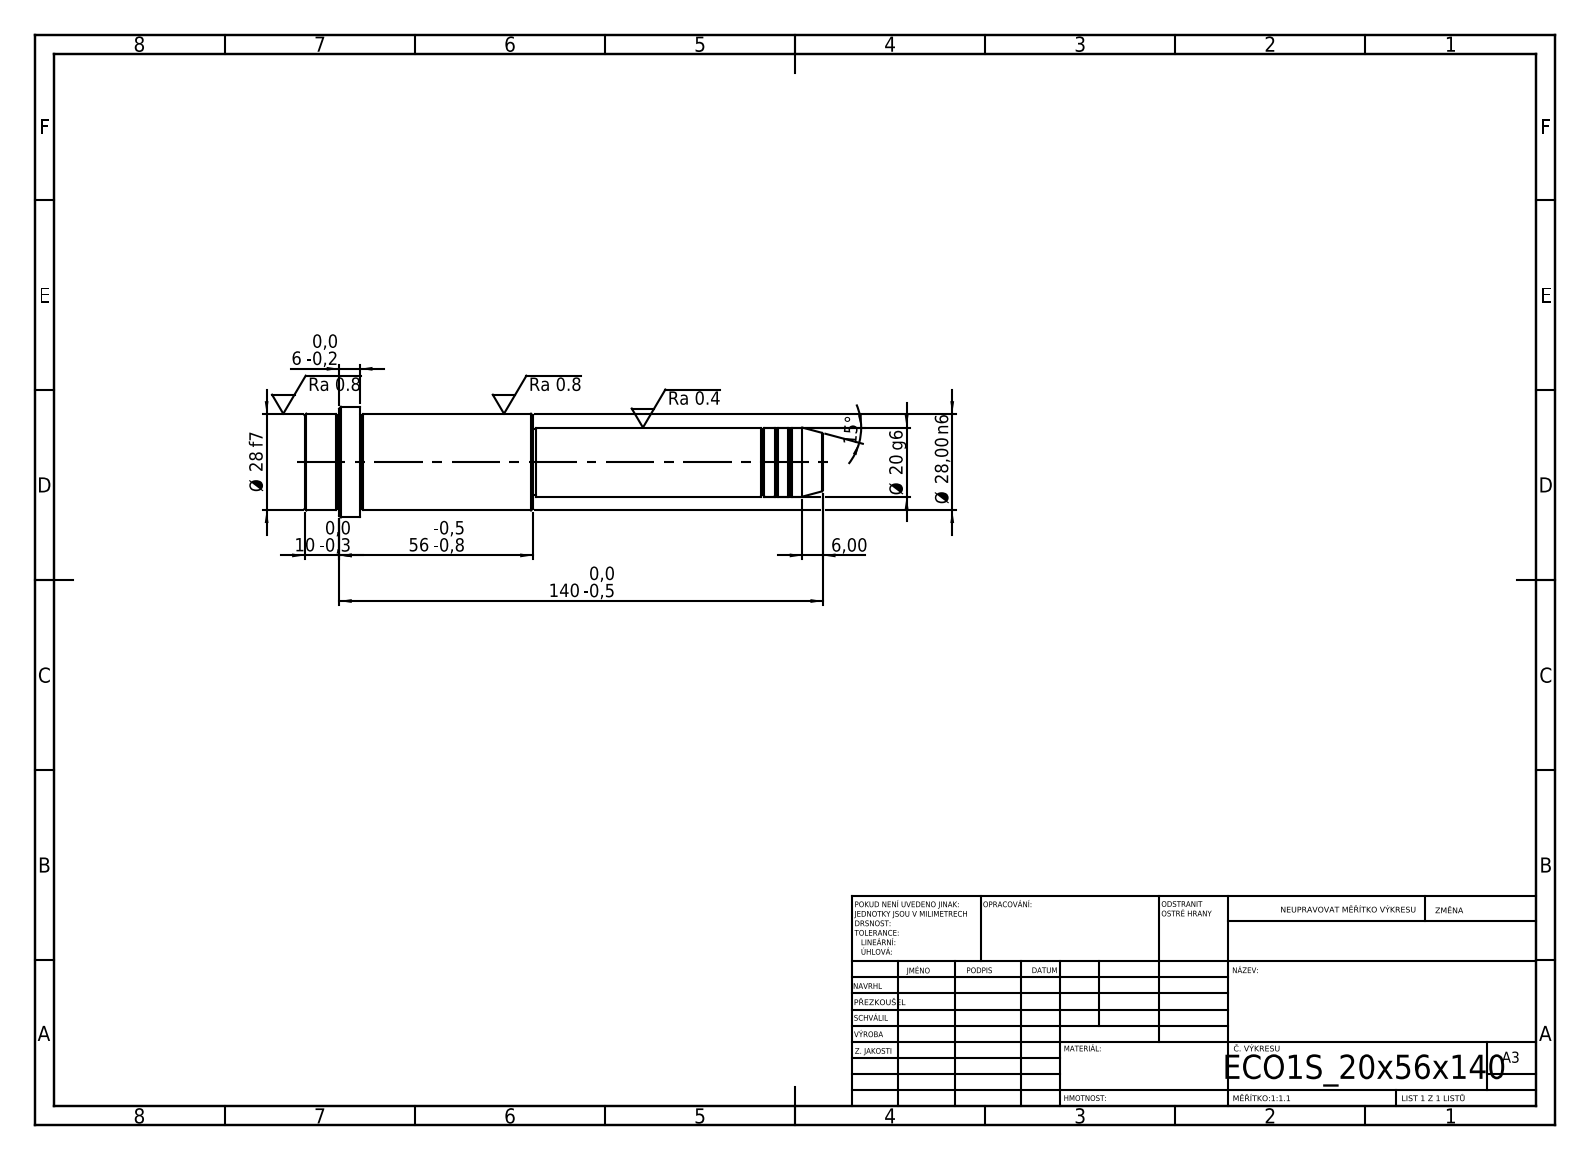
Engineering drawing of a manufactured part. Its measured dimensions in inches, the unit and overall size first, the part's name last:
Units: inches
Overall size (bounding box): 5.906 × 1.26 × 1.26
Round bosses / shafts (diameter × count): ⌀1.26 ×1, ⌀1.102 ×1, ⌀0.787 ×1, ⌀0.748 ×1
Main face-to-face distances: 2.598, 3.307, 5.906, 5.276, 1.969, 0.63, 5.512, 2.205, 0.236, 0.394
Volume: 4.129 in³ · Surface area: 19.87 in²
Bodies: 1 solid, 52 faces (6 planar, 16 cylindrical, 30 other)
STEP written by: SolidWorks 2019 (CONFIG_CONTROL_DESIGN)
